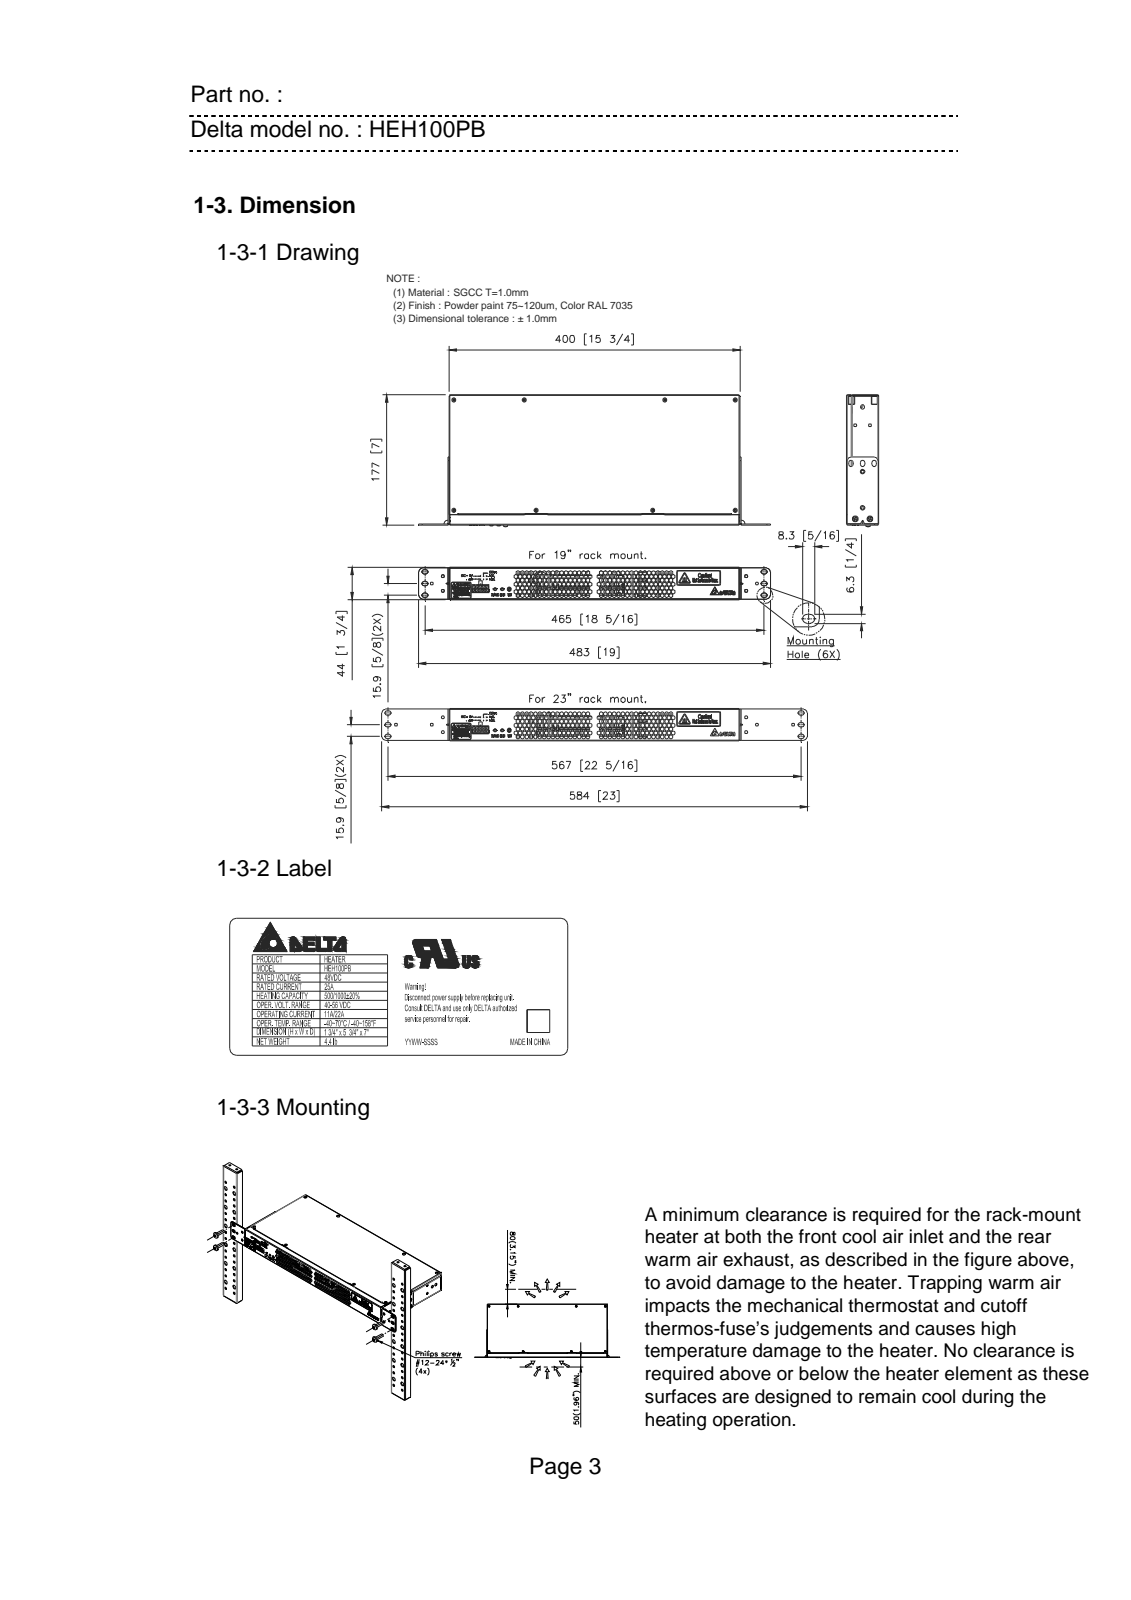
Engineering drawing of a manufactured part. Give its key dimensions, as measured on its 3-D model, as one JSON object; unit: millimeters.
{"part_name": "HEH100PB_CASE-1-SOLID1; HEH100PB_CASEIIIIITT5E5T4E-10-S; HEH100PB_CASEIIIIITT5E5T4E-9-SO; HEH100PB-001_VX01_1_ASM", "step_written_by": "CREO PARAMETRIC BY PTC INC, 2015080 (CONFIG_CONTROL_DESIGN)", "units": "millimeters", "bodies": {"solids": 3, "faces": 3164, "planar": 2842, "cylindrical": 166, "other": 156}, "overall_size": [482.61, 177.51, 44], "volume_mm3": 3122000, "surface_area_mm2": 217938, "round_holes": [[4.3, 6], [4, 4], [4.1, 2], [6, 1], [6.3, 1]], "round_bosses_or_shafts": [[1.5, 10], [6, 2], [6.07, 1]], "partial_cylinders_radius": [[3.15, 18], [1.01, 13], [5, 6], [4.46, 4], [7.54, 4], [0.77, 3], [0.2, 2], [1.5, 2]], "face_to_face_distances": [44, 177.21, 1.5, 0.5, 176.71, 399, 400.51, 399.01, 400.5, 1.51], "hole_center_spacings": [20, 26.93, 102.49, 127, 128.57, 416.01, 416.49, 8]}
